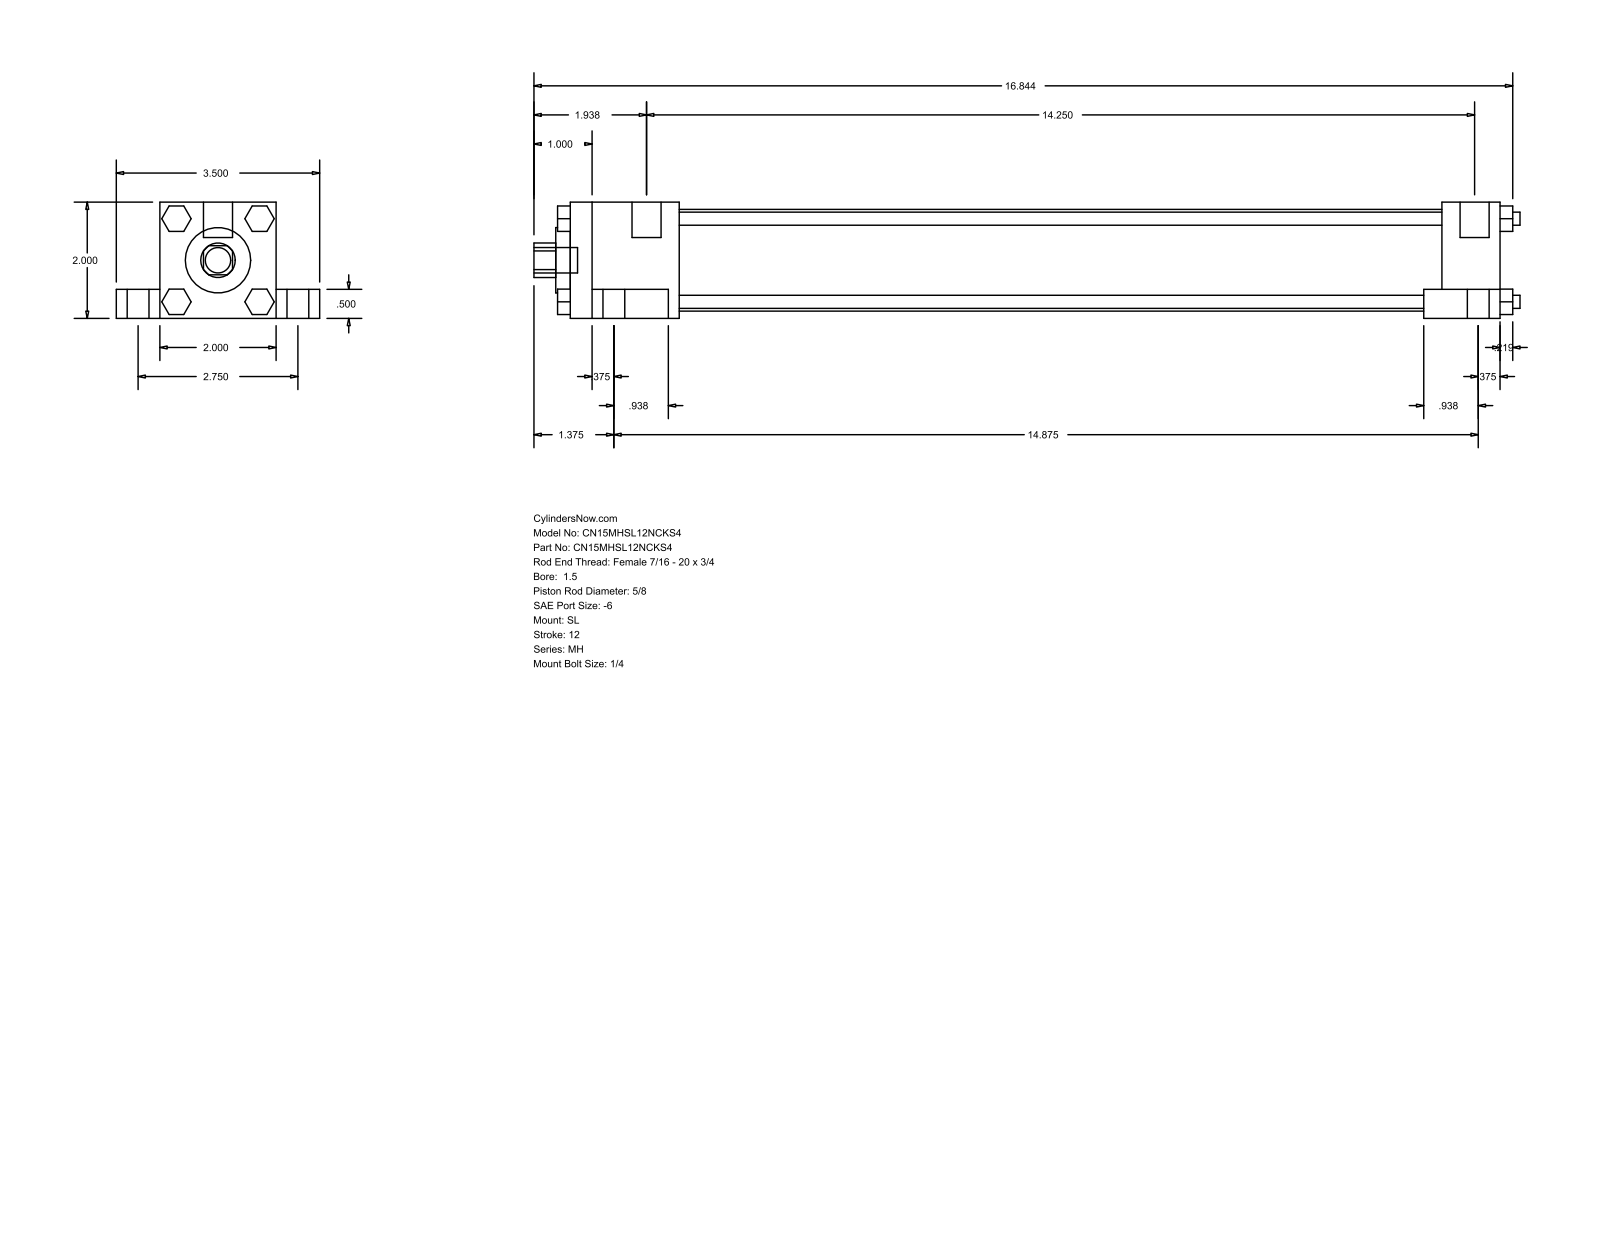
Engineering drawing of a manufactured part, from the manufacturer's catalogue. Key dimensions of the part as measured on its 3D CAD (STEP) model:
Part name (STEP PRODUCT): MH_SL__0150_0.625
STEP written by: GSSL Pune (CONFIG_CONTROL_DESIGN)
Units: millimetres
Bodies: 0 solids, 148 faces (112 planar, 36 cylindrical, 0 other)
Overall size (bounding box): 431.01 × 88.9 × 50.8
Round holes (diameter × count): ⌀15.88 ×1, ⌀28.57 ×1, ⌀44.45 ×1
Round bosses / shafts (diameter × count): ⌀15.88 ×4, ⌀9.53 ×4, ⌀5.71 ×4, ⌀5.56 ×4, ⌀12.7 ×2, ⌀11.11 ×1
Partial cylindrical surfaces — rounded edges, fillets, slot ends (radius × count): R7.54 ×1
Main face-to-face distances: 50.8, 38.1, 19.05, 12.7, 69.85, 406.39, 9.52, 381, 25.39, 47.62
